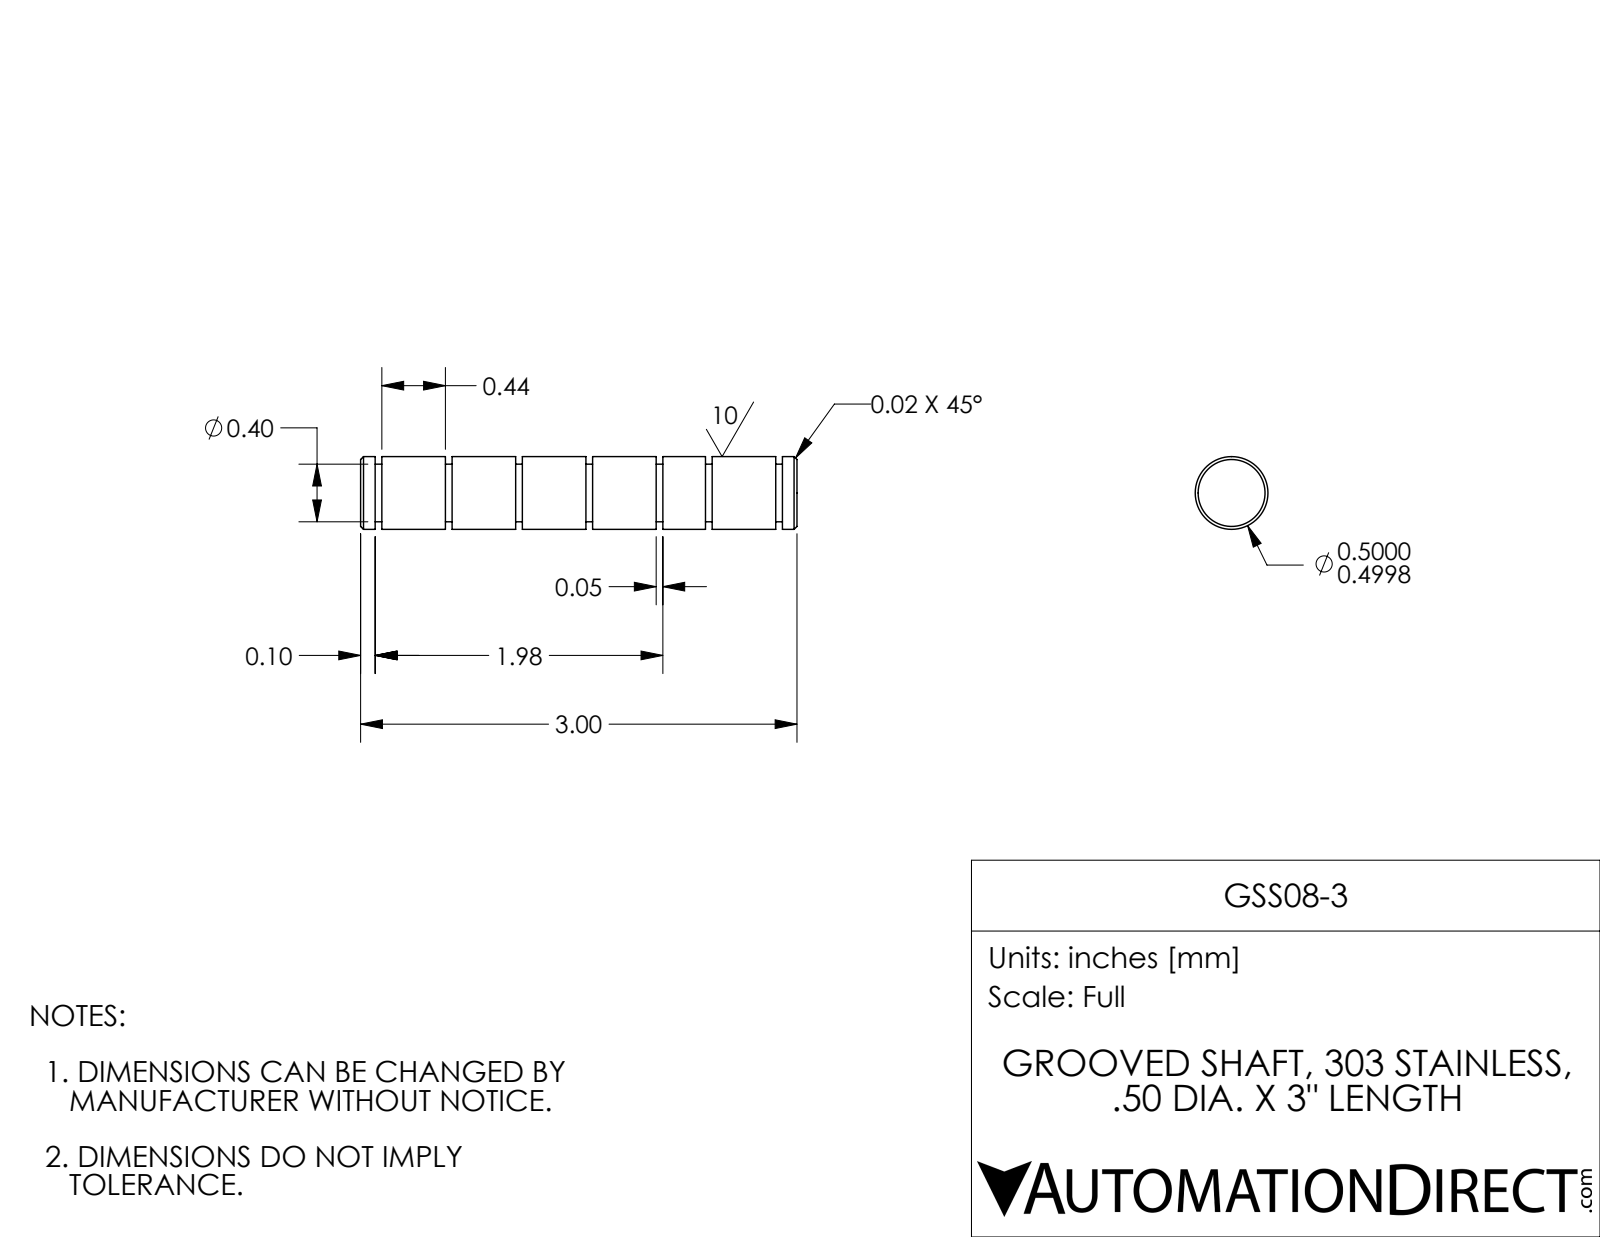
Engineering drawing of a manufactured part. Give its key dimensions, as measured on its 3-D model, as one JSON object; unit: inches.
{"part_name": "GSS08-3", "step_written_by": "SolidWorks 2017 (AUTOMOTIVE_DESIGN)", "units": "inches", "bodies": {"solids": 1, "faces": 50, "planar": 16, "cylindrical": 30, "other": 4}, "overall_size": [3, 0.5, 0.5], "volume_in3": 0.565, "surface_area_in2": 5.987, "round_bosses_or_shafts": [[0.5, 1], [0.396, 1]], "face_to_face_distances": [0.483, 0.046, 0.437, 1.449, 2.271, 0.822, 0.966, 0.529, 1.012, 1.788]}
